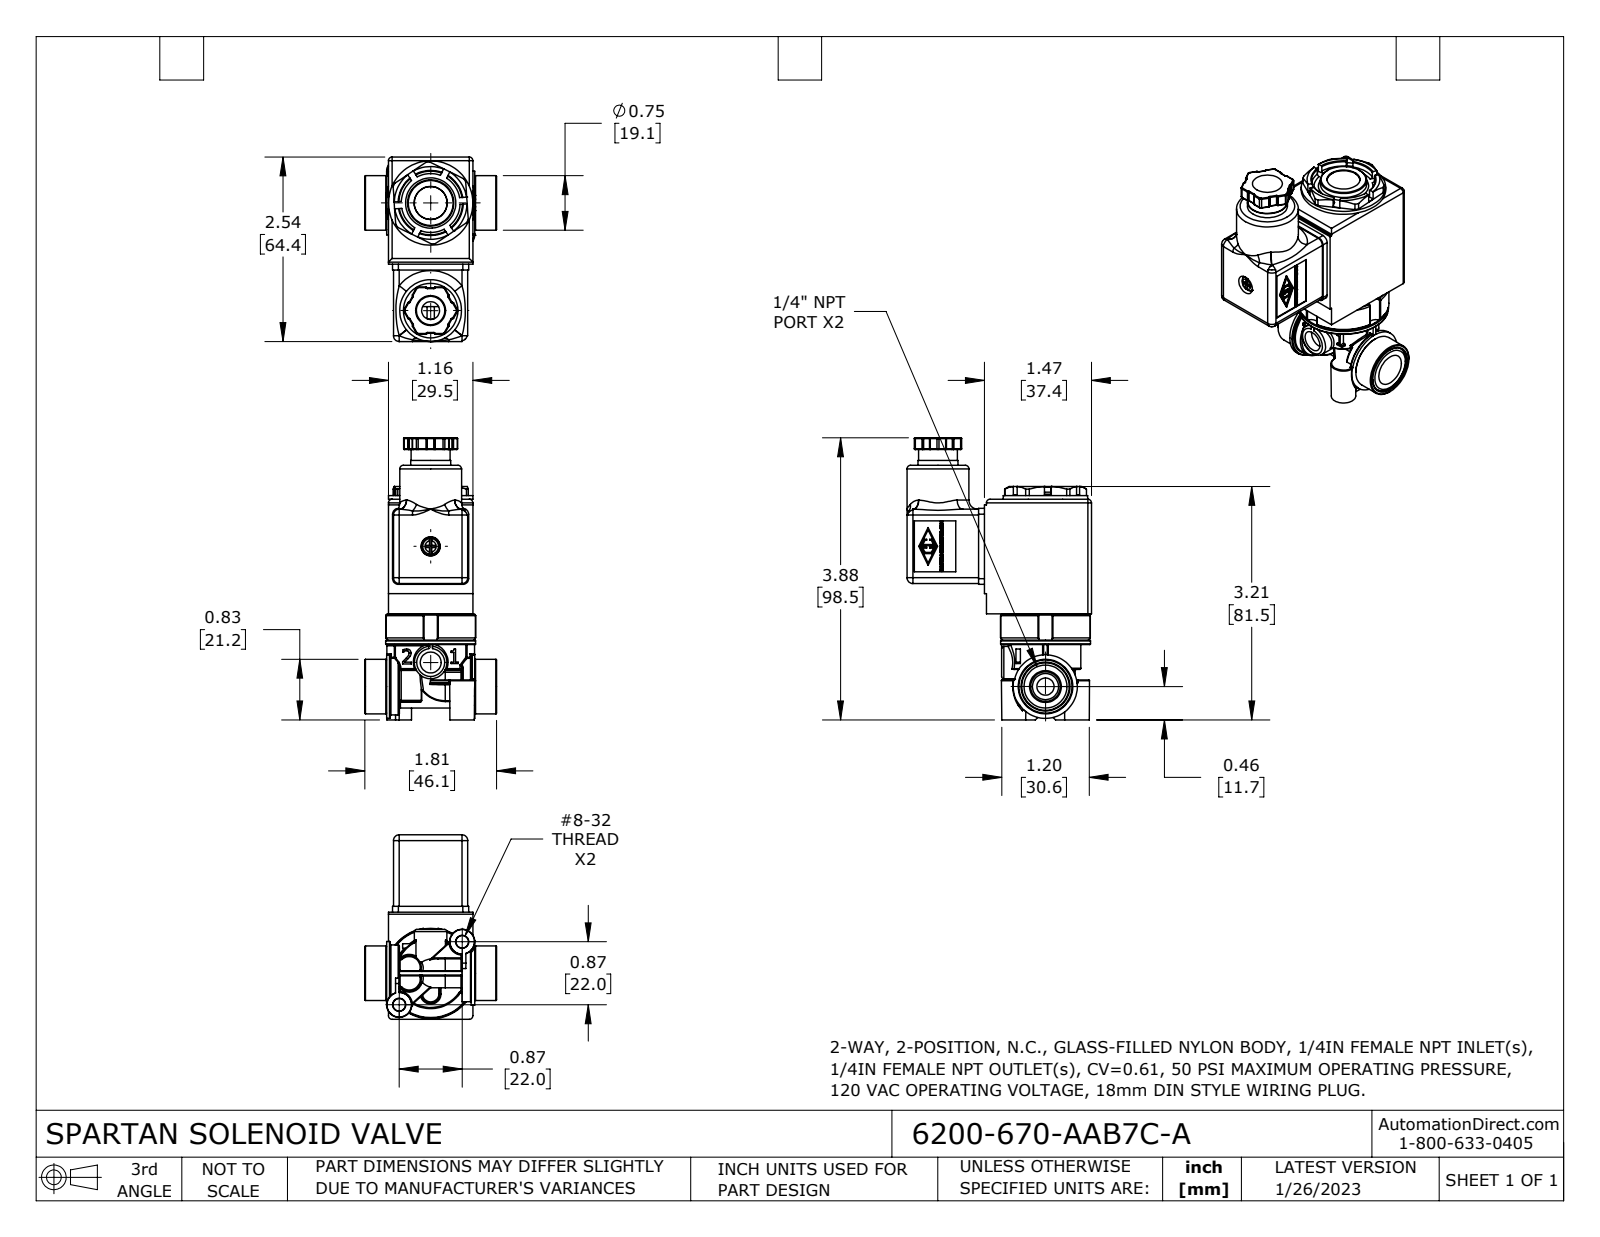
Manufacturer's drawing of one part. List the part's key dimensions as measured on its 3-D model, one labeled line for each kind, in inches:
Part name (STEP PRODUCT): 6200-670-AAB7C-A
STEP written by: SolidWorks 2021 (CONFIG_CONTROL_DESIGN)
Units: inches
Bodies: 4 solids, 1783 faces (801 planar, 328 cylindrical, 654 other)
Overall size (bounding box): 3.878 × 2.536 × 1.813
Volume: 4.356 in³ · Surface area: 55.75 in²
Round holes (diameter × count): ⌀0.236 ×2, ⌀0.053 ×1, ⌀0.06 ×1, ⌀0.095 ×1, ⌀0.102 ×1, ⌀0.12 ×1, ⌀0.203 ×1, ⌀0.245 ×1, ⌀0.25 ×1, ⌀0.263 ×1, ⌀0.287 ×1, ⌀0.39 ×1
Round bosses / shafts (diameter × count): ⌀1.236 ×1, ⌀1.16 ×1, ⌀1 ×1, ⌀0.972 ×1, ⌀0.875 ×1, ⌀0.875 ×1, ⌀0.85 ×1, ⌀0.78 ×1
Partial cylindrical surfaces — rounded edges, fillets, slot ends (radius × count): R0.01 ×69, R0.015 ×38, R0.05 ×14, R0.08 ×12, R0.03 ×6, R0.008 ×4, R0.02 ×4, R0.04 ×4
Main face-to-face distances: 1.161, 0.925, 1.472, 0.039, 0.08, 0.917, 0.048, 0.973, 0.079, 0.118
Hole centre spacings: 0.281, 0.352, 1.127, 1.408, 1.478, 1.595, 1.759, 2.211
